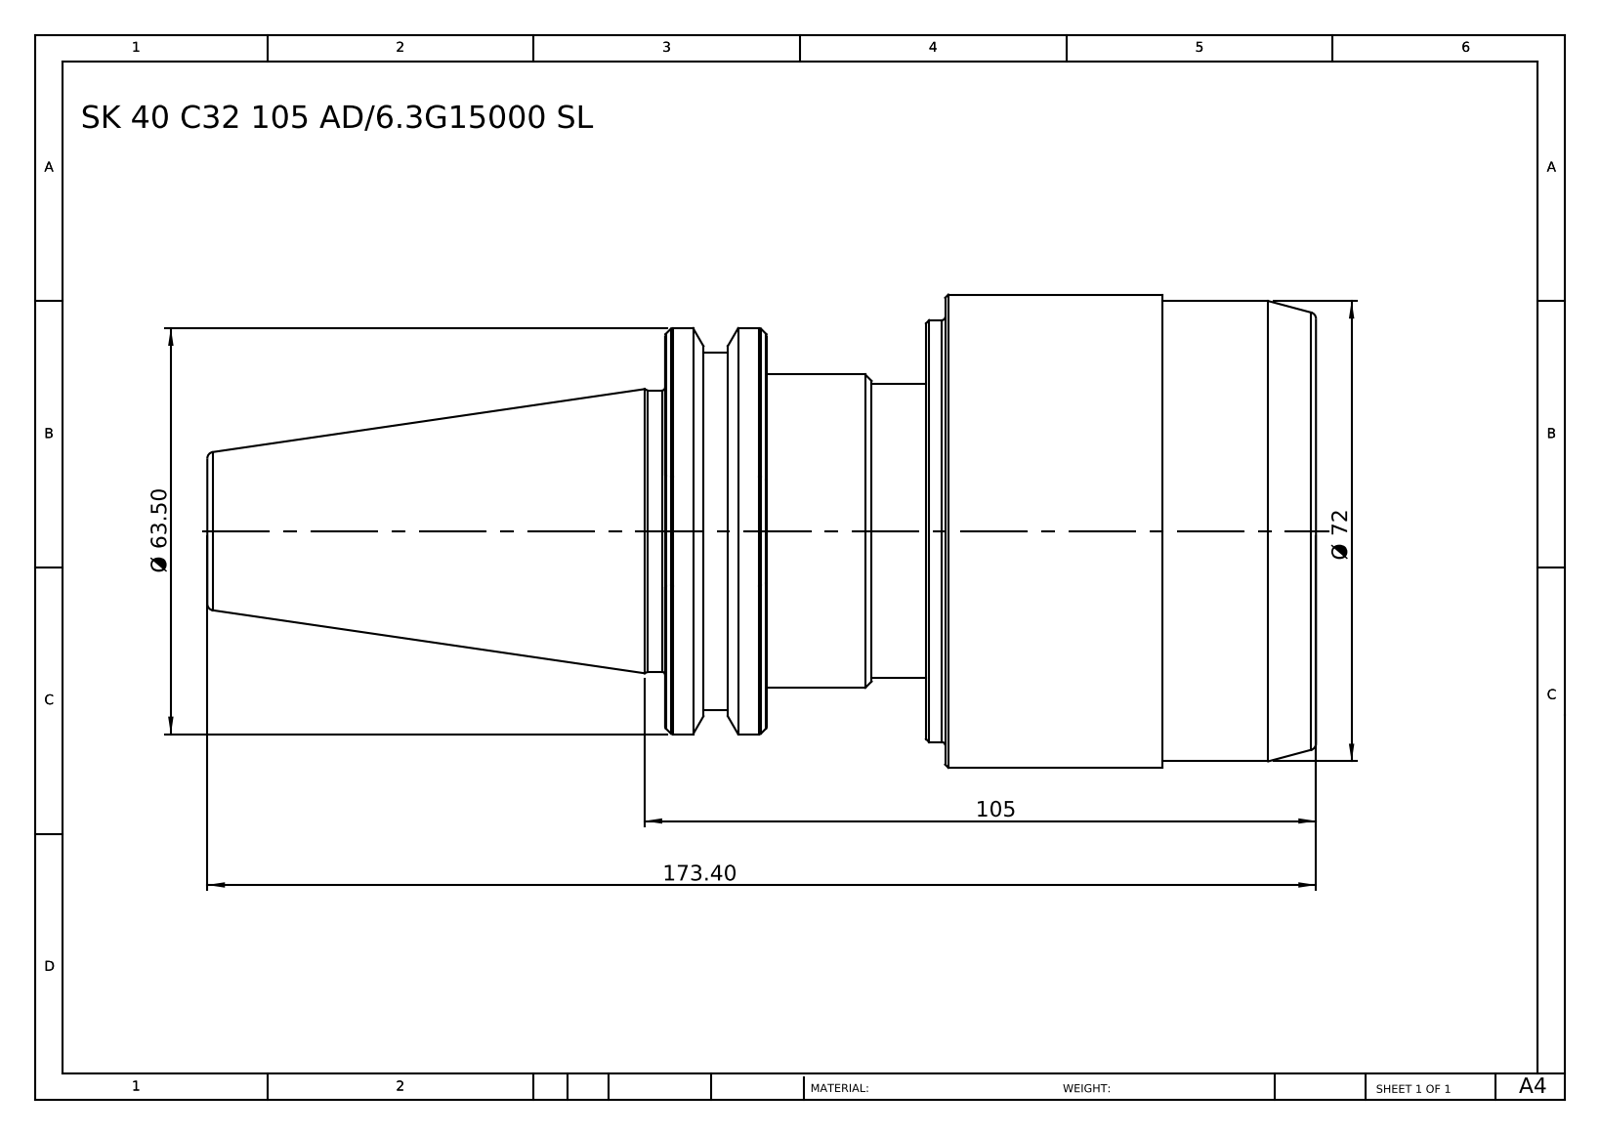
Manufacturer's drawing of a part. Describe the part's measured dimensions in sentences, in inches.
The part is named "SK 40 C32 105 AD-6.3G15000 SL". Its 3-D file was written by "SolidWorks 2014 (CONFIG_CONTROL_DESIGN)". It is 1 solid with 84 faces: 10 planar, 18 cylindrical and 56 other. Overall it measures 6.827 by 2.913 by 2.913 inches. Its volume is 25.3 cubic inches and its surface area 60.72 square inches. Round bosses or shafts: 1 of diameter 2.913, 1 of diameter 2.835, 1 of diameter 2.598, 1 of diameter 2.5, 1 of diameter 2.205, 1 of diameter 1.929, 1 of diameter 1.811, 1 of diameter 1.732. The main face-to-face distances are 2.402, 4.008, 1.606, 3.382, 0.98, 0.626, 2.283, 0.118, 1.098, 1.724.
